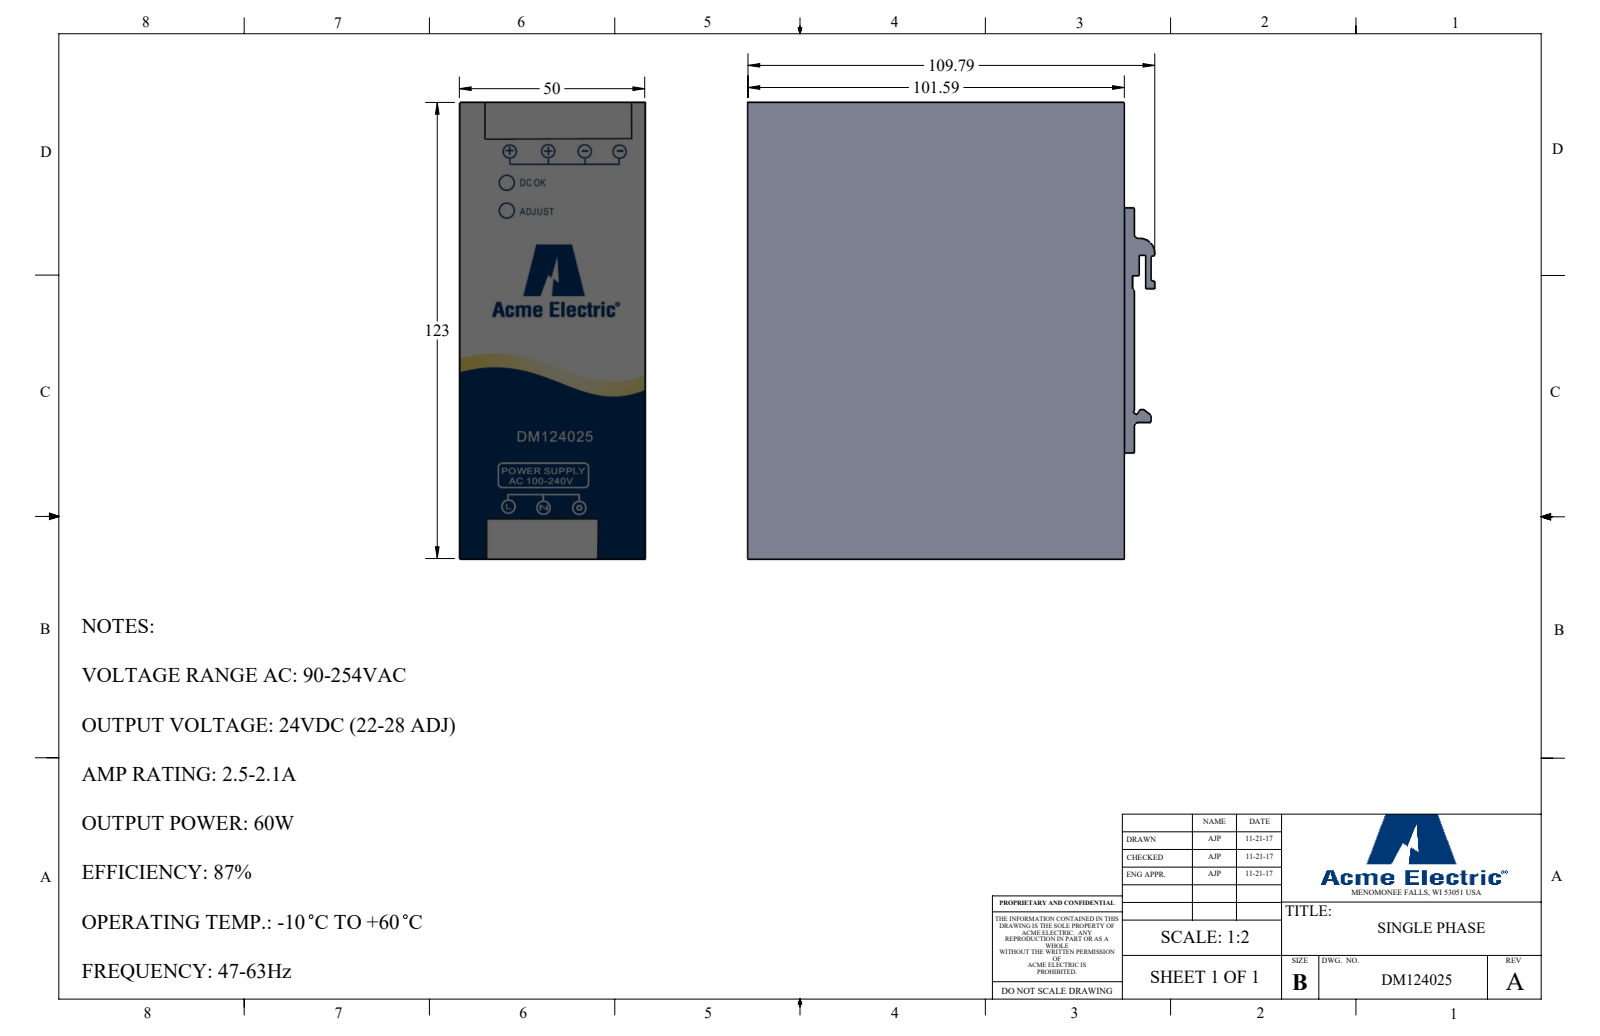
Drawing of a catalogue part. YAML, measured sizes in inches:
part_name: "DM124025"
step_written_by: "SolidWorks 2017 (AUTOMOTIVE_DESIGN)"
units: inches
bodies: {solids: 1, faces: 36, planar: 33, cylindrical: 3, other: 0}
overall_size: [4.843, 4.322, 1.969]
volume: 38.78
surface_area: 77.43
partial_cylinders:
  - {radius: 0.039, count: 2}
  - {radius: 0.157, count: 1}
face_to_face_distances: [1.969, 4.843, 4, 0.106, 4.106, 0.079, 1.89, 0.118, 0.224, 4.224]
